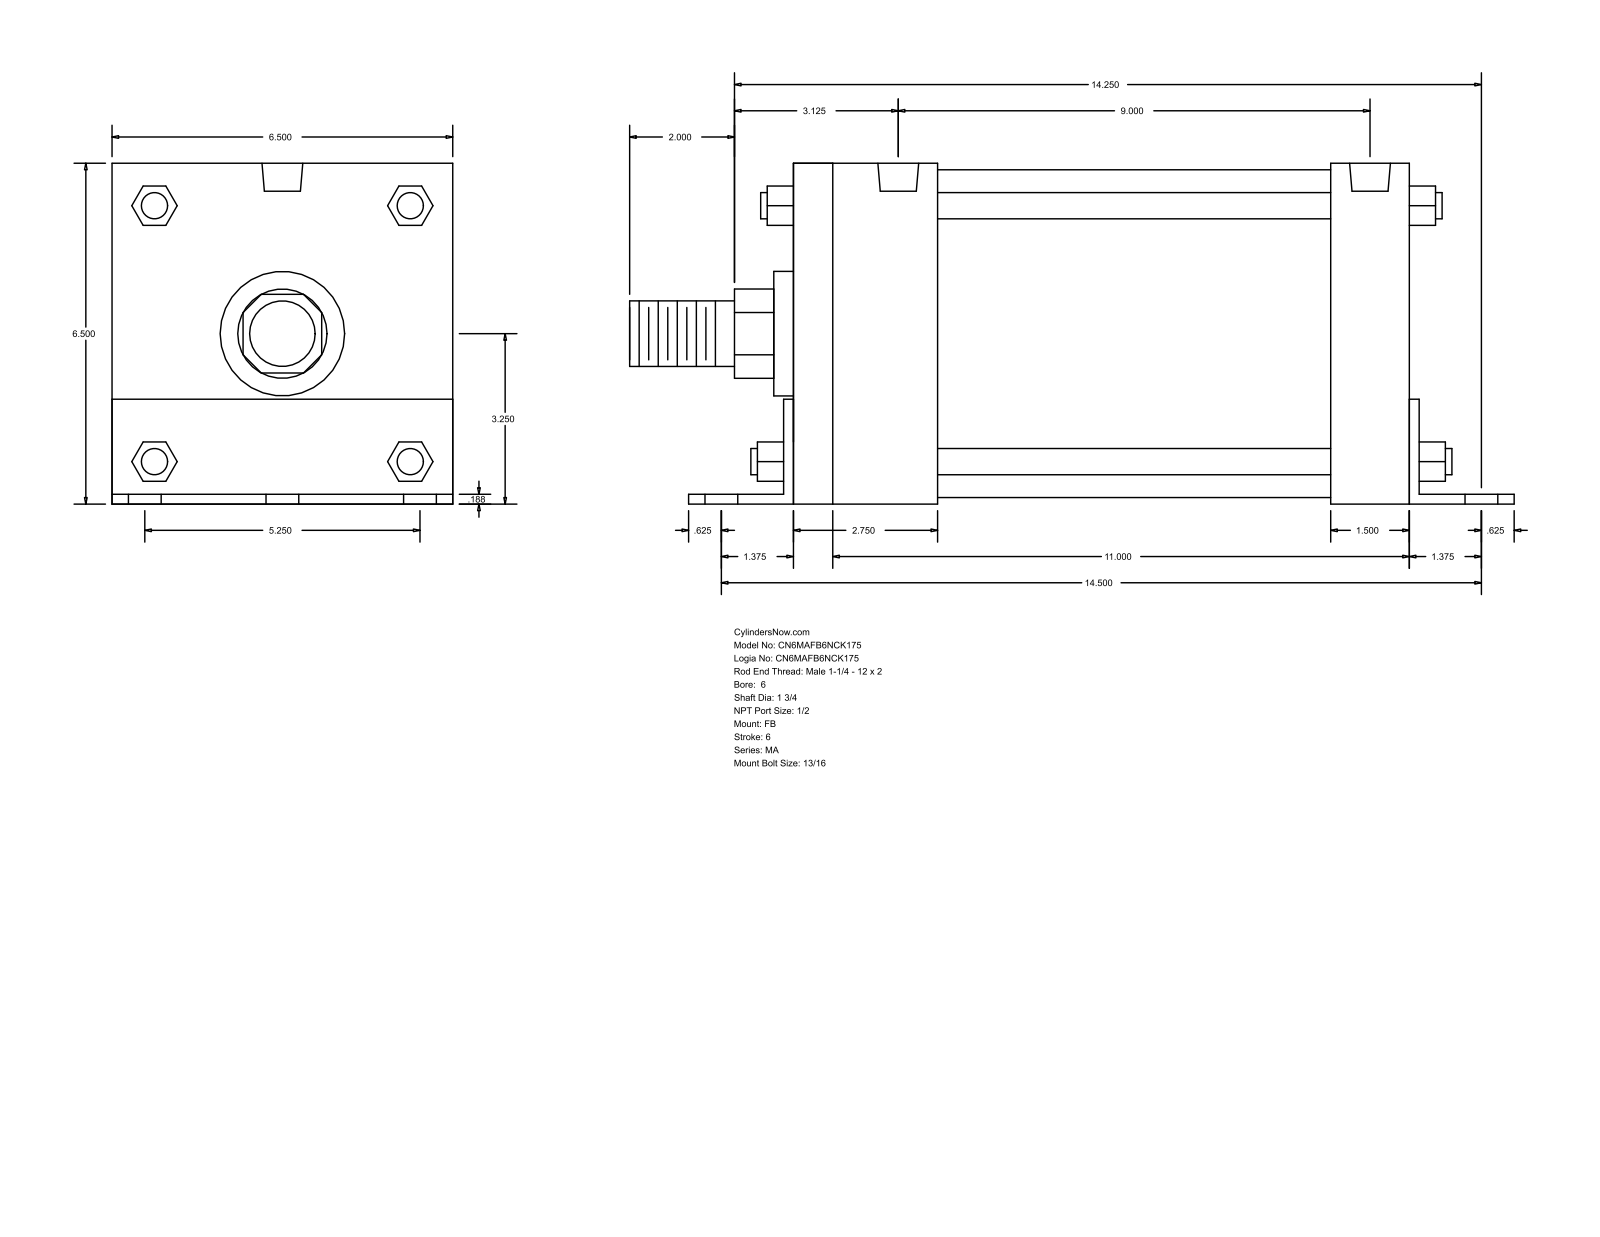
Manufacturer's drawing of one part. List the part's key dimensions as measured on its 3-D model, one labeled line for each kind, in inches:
Part name (STEP PRODUCT): MA_FB__0600_1.75
STEP written by: GSSL Pune (CONFIG_CONTROL_DESIGN)
Units: inches
Bodies: 0 solids, 140 faces (105 planar, 35 cylindrical, 0 other)
Overall size (bounding box): 16.875 × 6.502 × 6.5
Round holes (diameter × count): ⌀0.813 ×6, ⌀0.687 ×4, ⌀0.778 ×2
Round bosses / shafts (diameter × count): ⌀0.5 ×4, ⌀6.25 ×1, ⌀2.375 ×1, ⌀1.75 ×1, ⌀1.25 ×1
Partial cylindrical surfaces — rounded edges, fillets, slot ends (radius × count): R0.852 ×1, R1.262 ×1
Main face-to-face distances: 6.5, 0.187, 11.75, 6.502, 0.185, 6.315, 2.75, 2.937, 0.188, 1.5
Hole centre spacings: 2.625, 14.736, 14.5, 3.377, 4.276, 5.25, 9, 11.43
